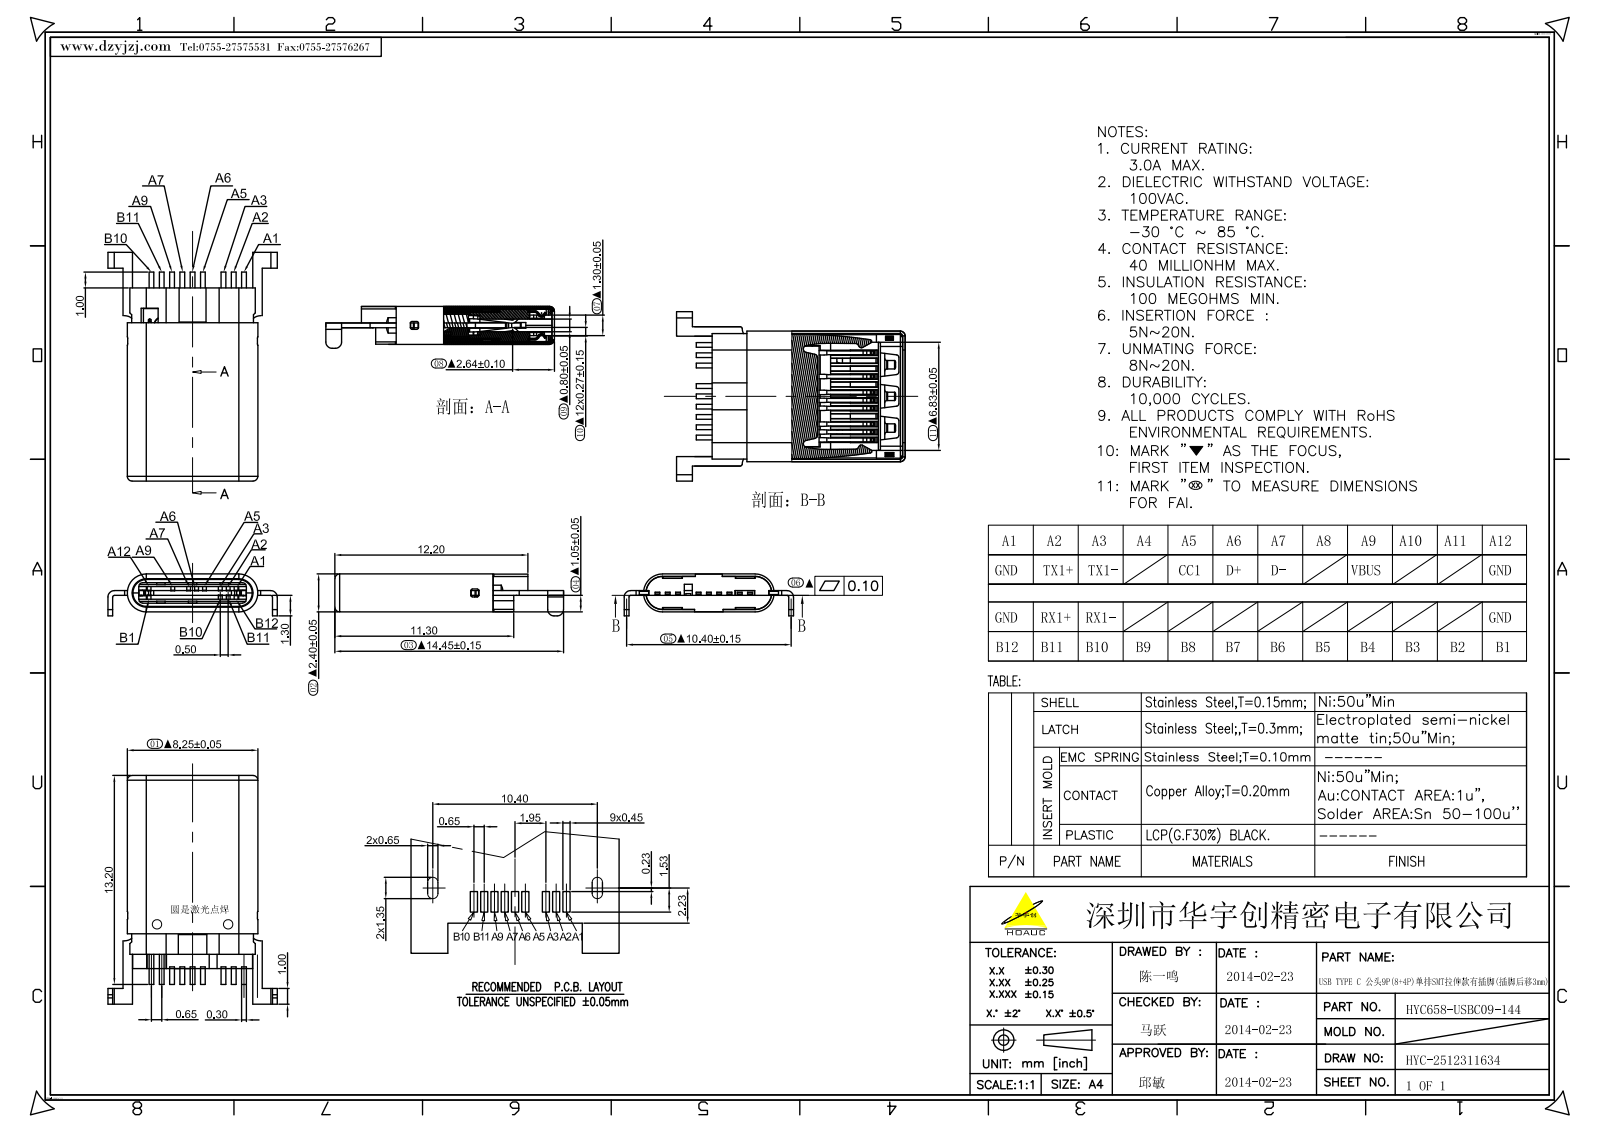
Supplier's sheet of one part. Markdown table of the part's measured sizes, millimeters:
| quantity | value |
| --- | --- |
| part name | XDS-A_TC_2_M_215D_ASM |
| STEP written by | CREO PARAMETRIC BY PTC INC, 2022073 (CONFIG_CONTROL_DESIGN) |
| units | millimeters |
| bodies | 1 solid, 405 faces (303 planar, 98 cylindrical, 4 other) |
| overall size | 14.45 × 10.7 × 2.65 |
| volume | 181 mm³ |
| surface area | 422 mm² |
| round holes (diameter × count) | 0.6 × 2 |
| partial cylindrical surfaces (radius × count) | 0.1 × 12, 0.15 × 12, 0.25 × 6, 0.3 × 6, 1.05 × 6, 0.4 × 4, 0.58 × 2, 0.6 × 2 |
| main face-to-face distances | 0.8, 2.4, 1.6, 1.05, 0.55, 1.35, 0.5, 1.85, 1.3, 0.52 |
| hole center spacings | 4.48 |
